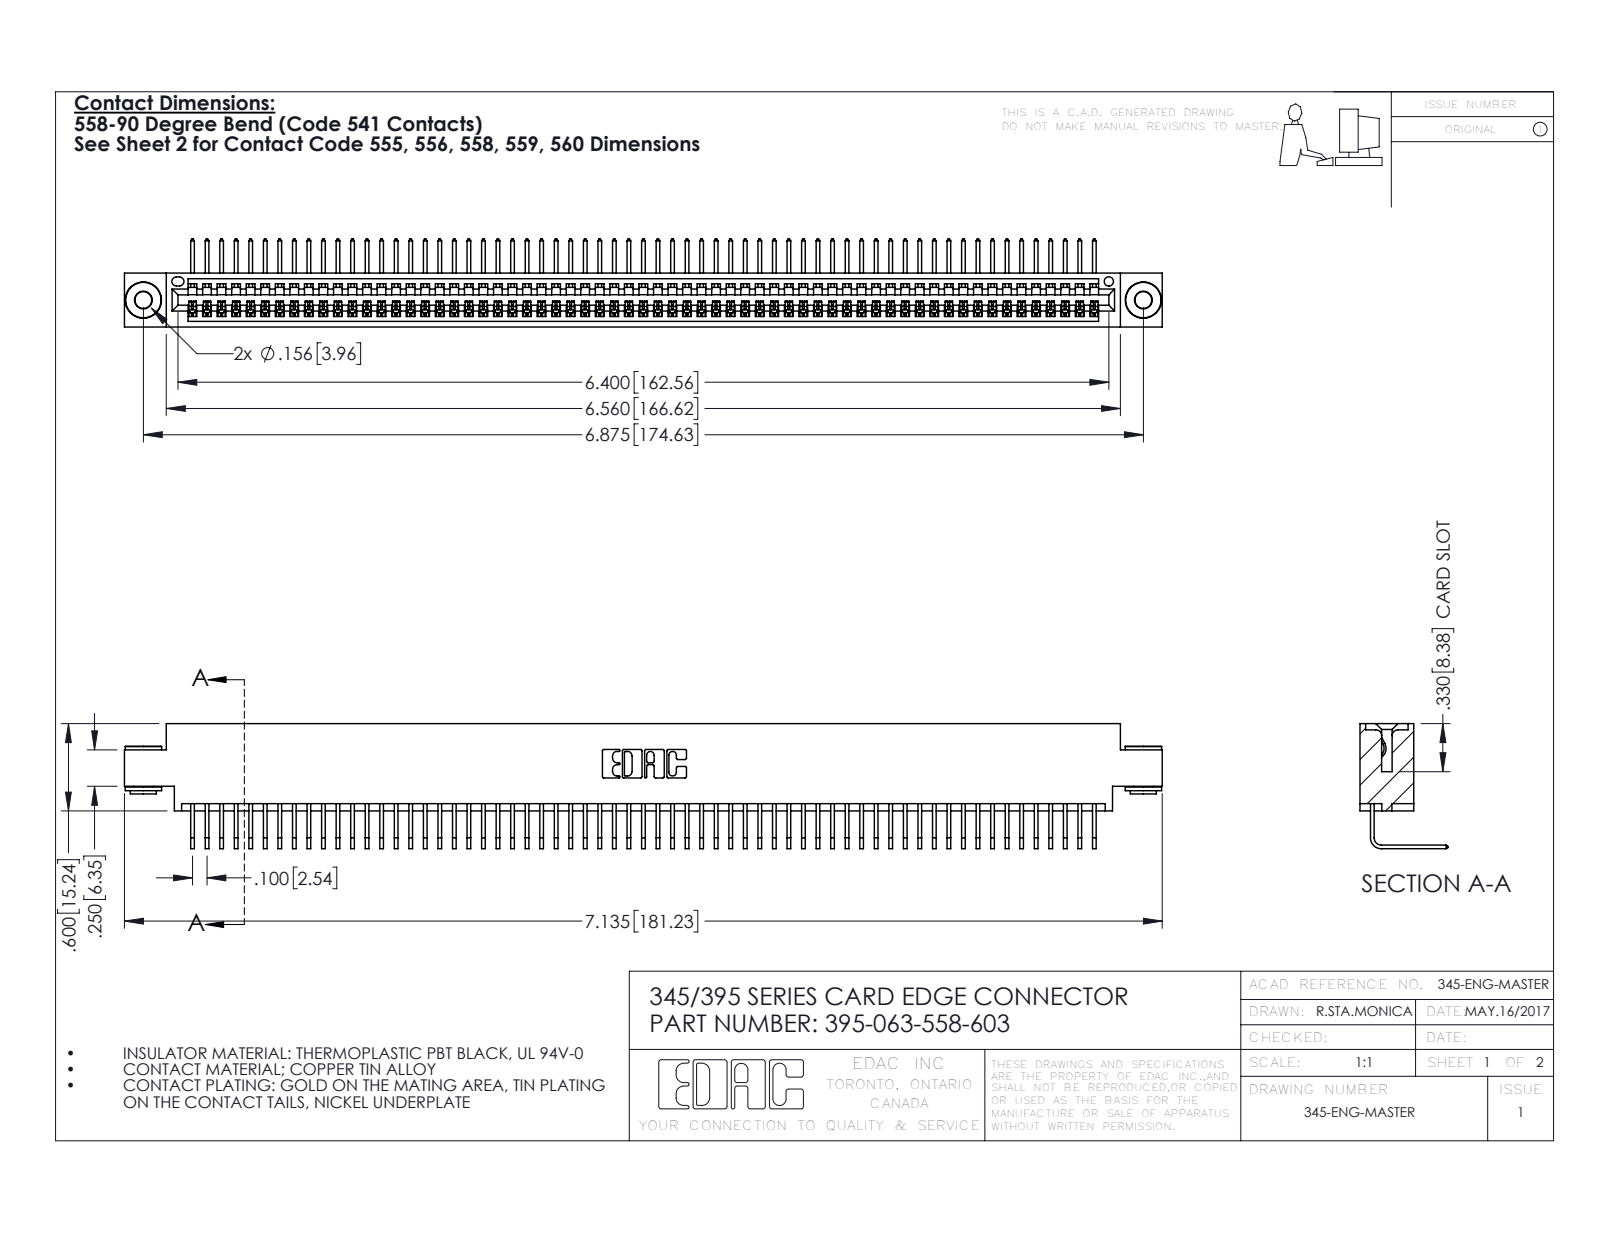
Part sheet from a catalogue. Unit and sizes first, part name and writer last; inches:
Units: inches
Overall size (bounding box): 7.135 × 0.859 × 0.605
Round holes (diameter × count): ⌀0.116 ×2, ⌀0.156 ×2, ⌀0.064 ×1
Round bosses / shafts (diameter × count): ⌀0.25 ×2, ⌀0.18 ×2, ⌀0.136 ×2
Partial cylindrical surfaces — rounded edges, fillets, slot ends (radius × count): R0.006 ×126, R0.01 ×22, R0.007 ×6, R0.031 ×6, R0.026 ×3, R0.031 ×2, R0.04 ×2, R0.014 ×1
Main face-to-face distances: 0.072, 0.298, 0.37, 0.2, 0.098, 0.272, 0.025, 0.225, 0.175, 0.149
Hole centre spacings: 0.27, 6.639, 6.875
Volume: 1.068 in³ · Surface area: 38.93 in²
Bodies: 66 solids, 3948 faces (2740 planar, 1200 cylindrical, 8 other)
Part name (STEP PRODUCT): 345-292-001_558 Tail - 2; 345-250-002_345-250-002-102; 345 Part_0.170 Offset - 0.156 Dia-TH; 395-063-558-603
STEP written by: SolidWorks 2016 (CONFIG_CONTROL_DESIGN)
